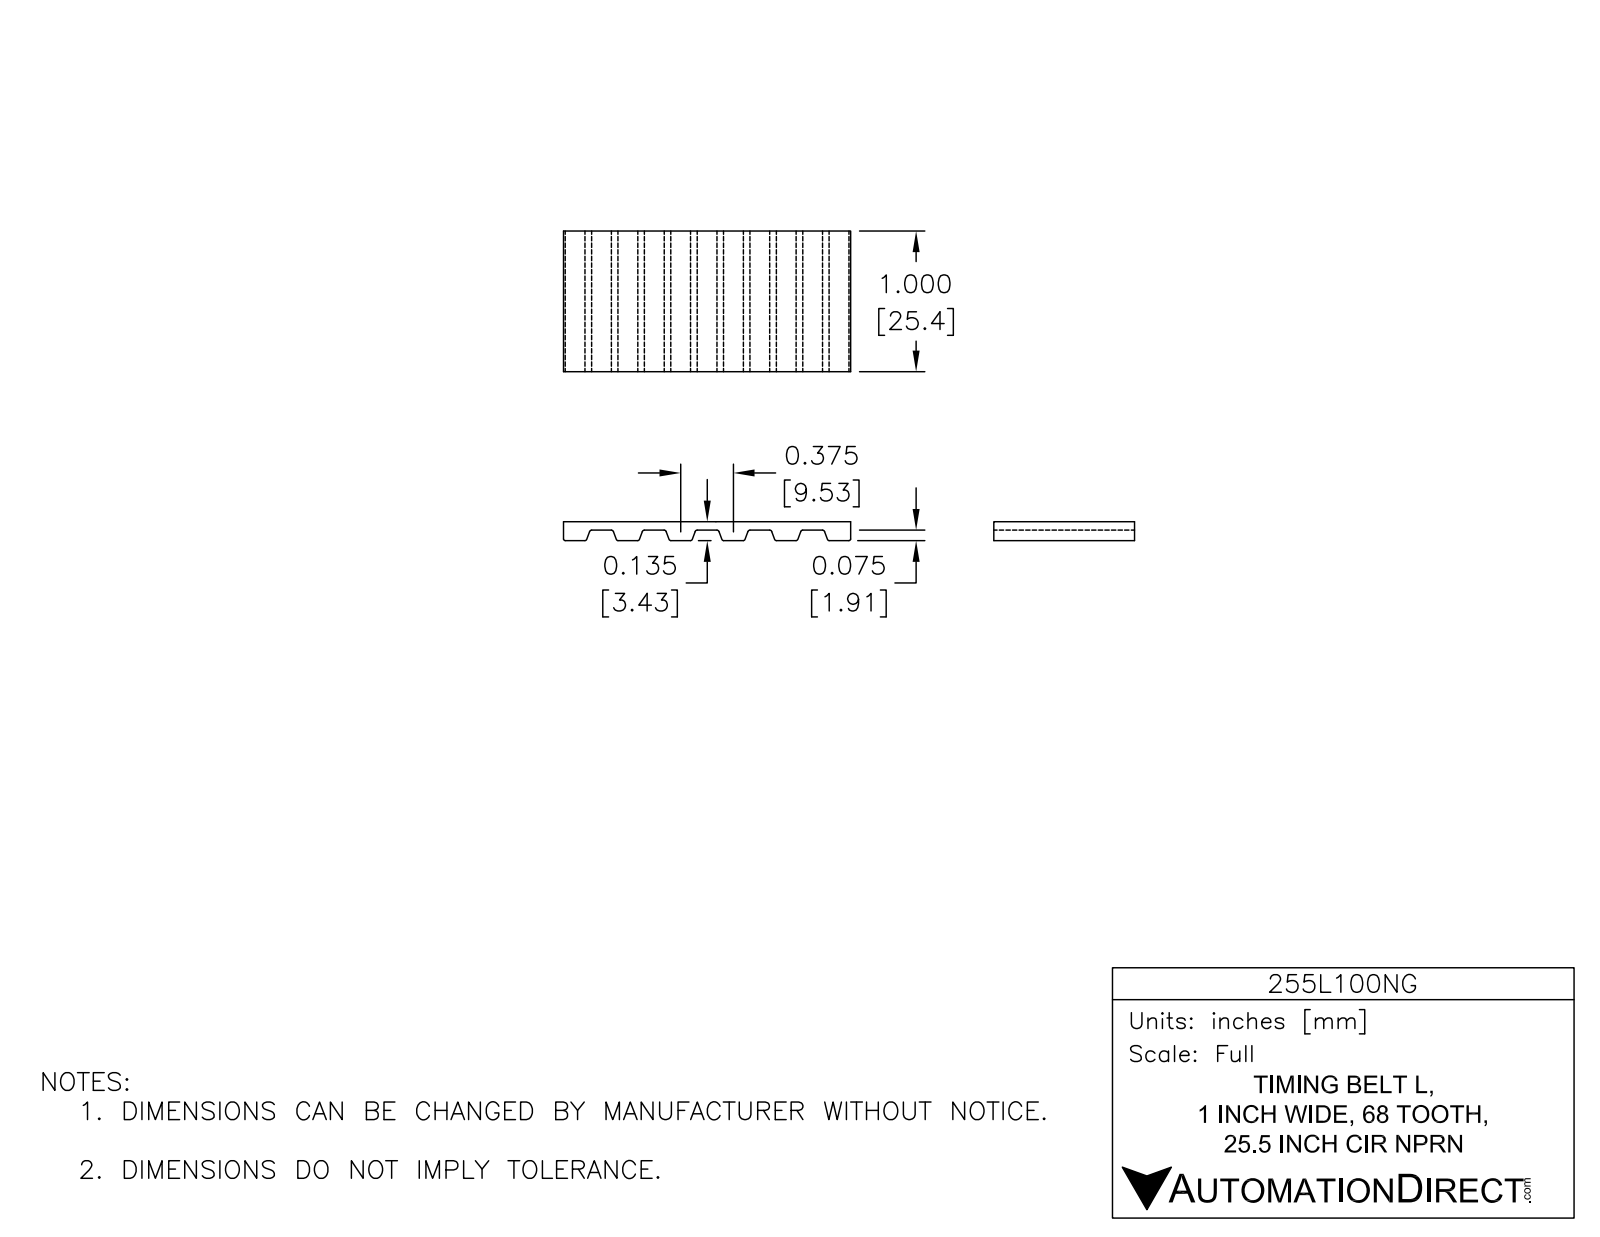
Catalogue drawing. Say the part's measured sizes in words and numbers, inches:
The part is named "255L100NG". Its 3-D file was written by "SolidWorks 2014 (AUTOMOTIVE_DESIGN)". It is 1 solid with 559 faces: 249 planar, 310 cylindrical and 0 other. Overall it measures 11.038 by 3 by 1 inches. Its volume is 2.301 cubic inches and its surface area 61.26 square inches. Partial cylindrical surfaces (rounded edges, fillets, slot ends): 268 of radius 0.02, 2 of radius 1.435, 2 of radius 1.5. The main face-to-face distances are 0.065, 2.935, 3, 2.87, 0.14, 2.86, 0.075, 2.795, 1, 2.72.
